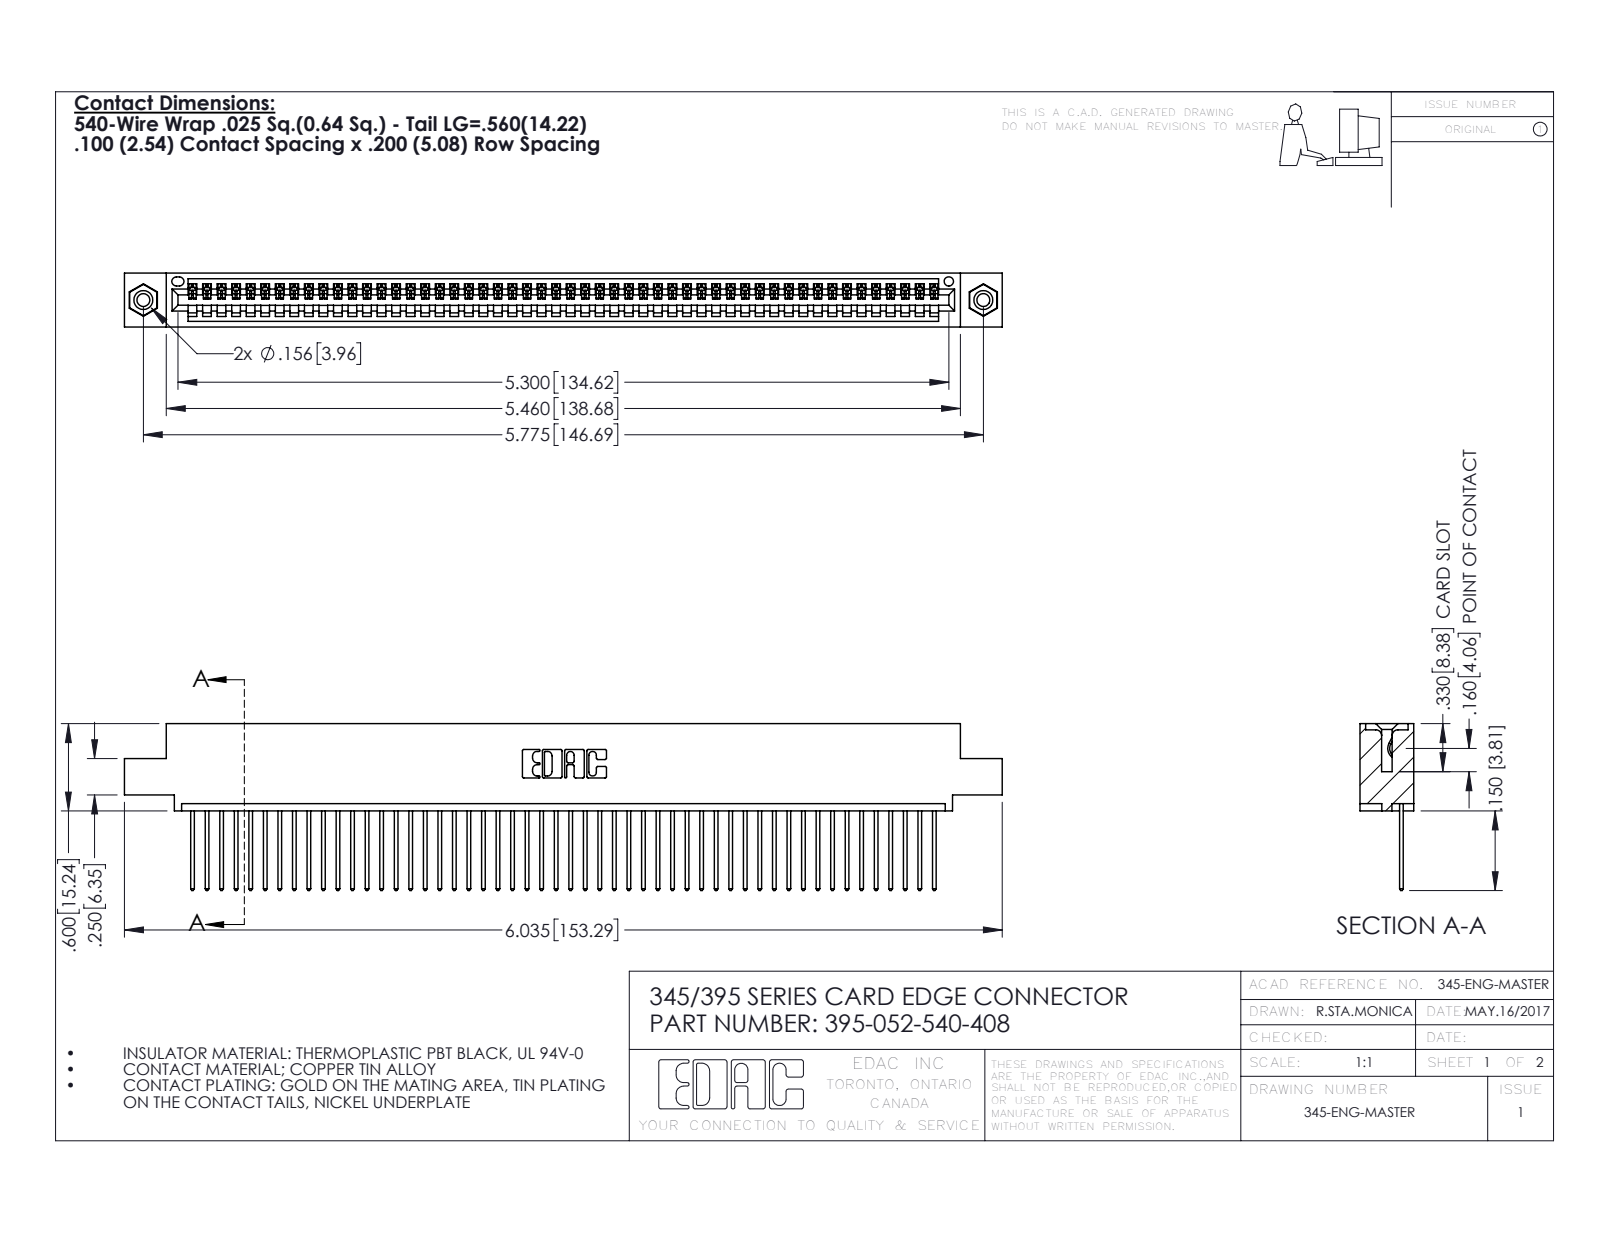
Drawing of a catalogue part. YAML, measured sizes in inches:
part_name: "345-292-001_345-293-140; 345 Part_0.110 Offset - 0.156 Dia-TI; 395-052-540-408; 345-250-001_345-250-003-102"
step_written_by: "SolidWorks 2016 (CONFIG_CONTROL_DESIGN)"
units: inches
bodies: {solids: 55, faces: 3206, planar: 2196, cylindrical: 994, other: 16}
overall_size: [6.035, 1.147, 0.37]
volume: 0.893
surface_area: 31.29
round_holes:
  - {diameter: 0.089, count: 2}
  - {diameter: 0.125, count: 2}
  - {diameter: 0.156, count: 2}
  - {diameter: 0.064, count: 1}
round_bosses_or_shafts:
  - {diameter: 0.155, count: 2}
partial_cylinders:
  - {radius: 0.006, count: 104}
  - {radius: 0.01, count: 104}
  - {radius: 0.01, count: 22}
  - {radius: 0.007, count: 6}
  - {radius: 0.031, count: 6}
  - {radius: 0.026, count: 3}
  - {radius: 0.031, count: 2}
  - {radius: 0.04, count: 2}
face_to_face_distances: [0.072, 0.298, 0.37, 0.098, 0.272, 0.025, 0.2, 0.225, 0.149, 0.072]
hole_center_spacings: [0.27, 5.539, 5.775]
